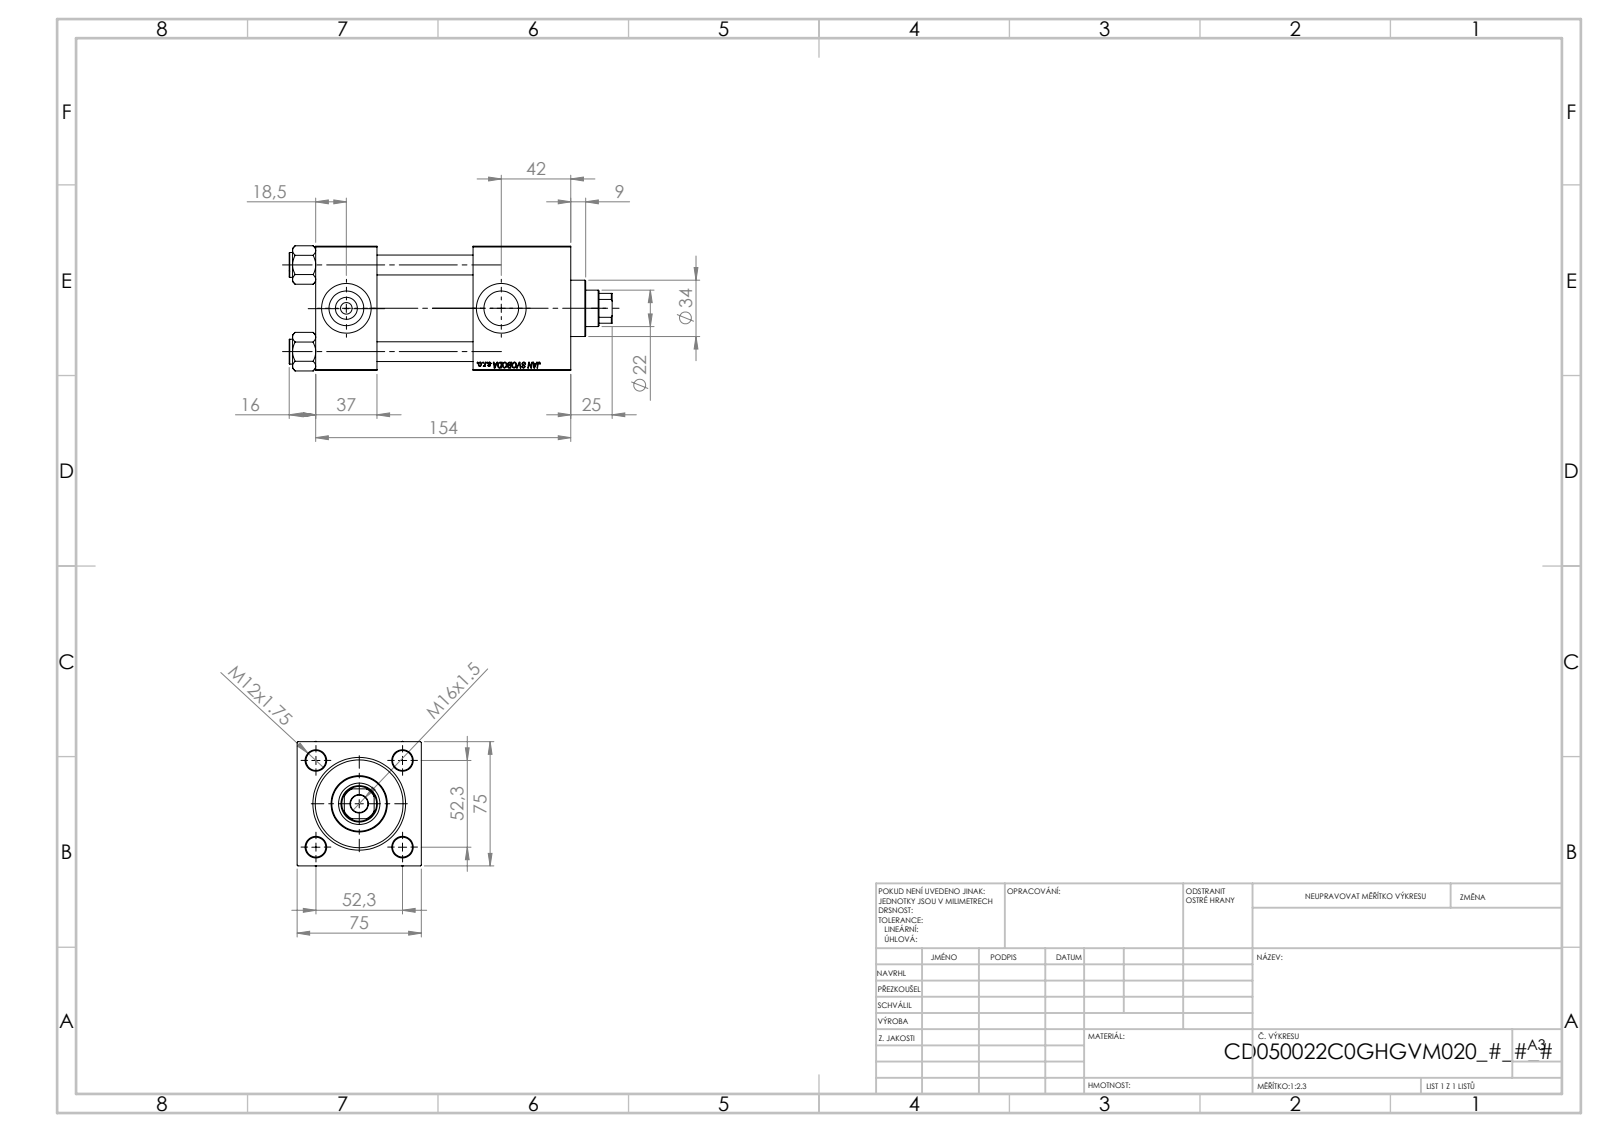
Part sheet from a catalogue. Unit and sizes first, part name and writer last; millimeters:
Units: millimetres
Overall size (bounding box): 195 × 75.54 × 75
Round holes (diameter × count): ⌀12 ×4, ⌀7 ×2, ⌀20.96 ×2, ⌀30 ×2, ⌀10.5 ×1, ⌀22 ×1, ⌀25 ×1, ⌀41 ×1, ⌀50 ×1, ⌀53 ×1
Round bosses / shafts (diameter × count): ⌀15 ×4, ⌀56 ×1, ⌀34 ×1
Partial cylindrical surfaces — rounded edges, fillets, slot ends (radius × count): R10.5 ×1
Main face-to-face distances: 75, 37, 154, 117, 95, 58, 59, 125.3, 88.3, 30.3
Hole centre spacings: 36.98, 52.3, 73.96, 93.5
Volume: 656 964 mm³ · Surface area: 147 285 mm²
Bodies: 11 solids, 1148 faces (526 planar, 86 cylindrical, 536 other)
Part name (STEP PRODUCT): V215CD_VC_C; V215CD_C_TYCINKA; NUT_M5_V215CD_C; V215CD_VCP_C (+1 more)
STEP written by: SolidWorks 2019 (CONFIG_CONTROL_DESIGN)
